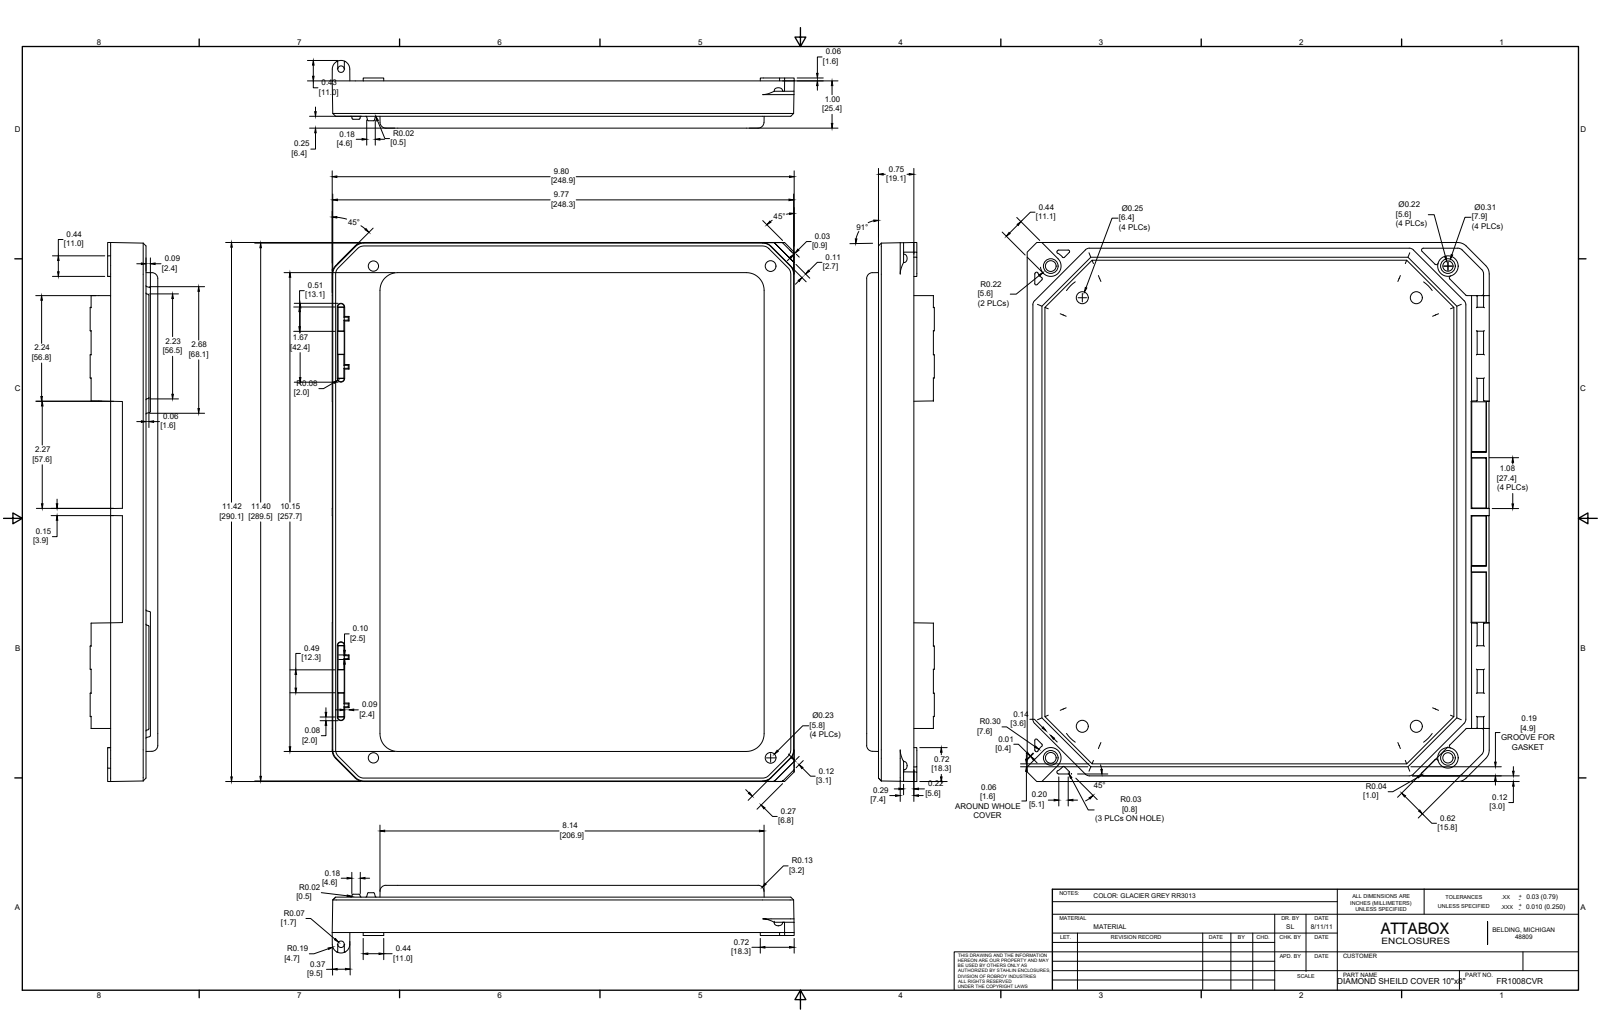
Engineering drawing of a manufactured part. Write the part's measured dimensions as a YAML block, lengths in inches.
part_name: "FR1008CVR"
step_written_by: "SolidWorks 2019 (AUTOMOTIVE_DESIGN)"
units: inches
bodies: {solids: 1, faces: 575, planar: 235, cylindrical: 192, other: 148}
overall_size: [11.423, 9.798, 1.434]
volume: 25.99
surface_area: 321.8
round_holes:
  - {diameter: 0.253, count: 4}
  - {diameter: 0.219, count: 2}
  - {diameter: 0.227, count: 2}
  - {diameter: 0.313, count: 2}
  - {diameter: 0.137, count: 1}
round_bosses_or_shafts:
  - {diameter: 0.435, count: 2}
partial_cylinders:
  - {radius: 0.03, count: 27}
  - {radius: 0.096, count: 16}
  - {radius: 0.062, count: 15}
  - {radius: 0.01, count: 14}
  - {radius: 0.125, count: 12}
  - {radius: 0.06, count: 11}
  - {radius: 0.04, count: 10}
  - {radius: 0.063, count: 9}
face_to_face_distances: [0.125, 0.25, 0.125, 0.75, 0.375, 0.375, 1, 0.625, 0.875, 0.625]
hole_center_spacings: [9.776, 0.946, 0.947, 7.084, 7.781, 7.783, 8.423, 9.084]
